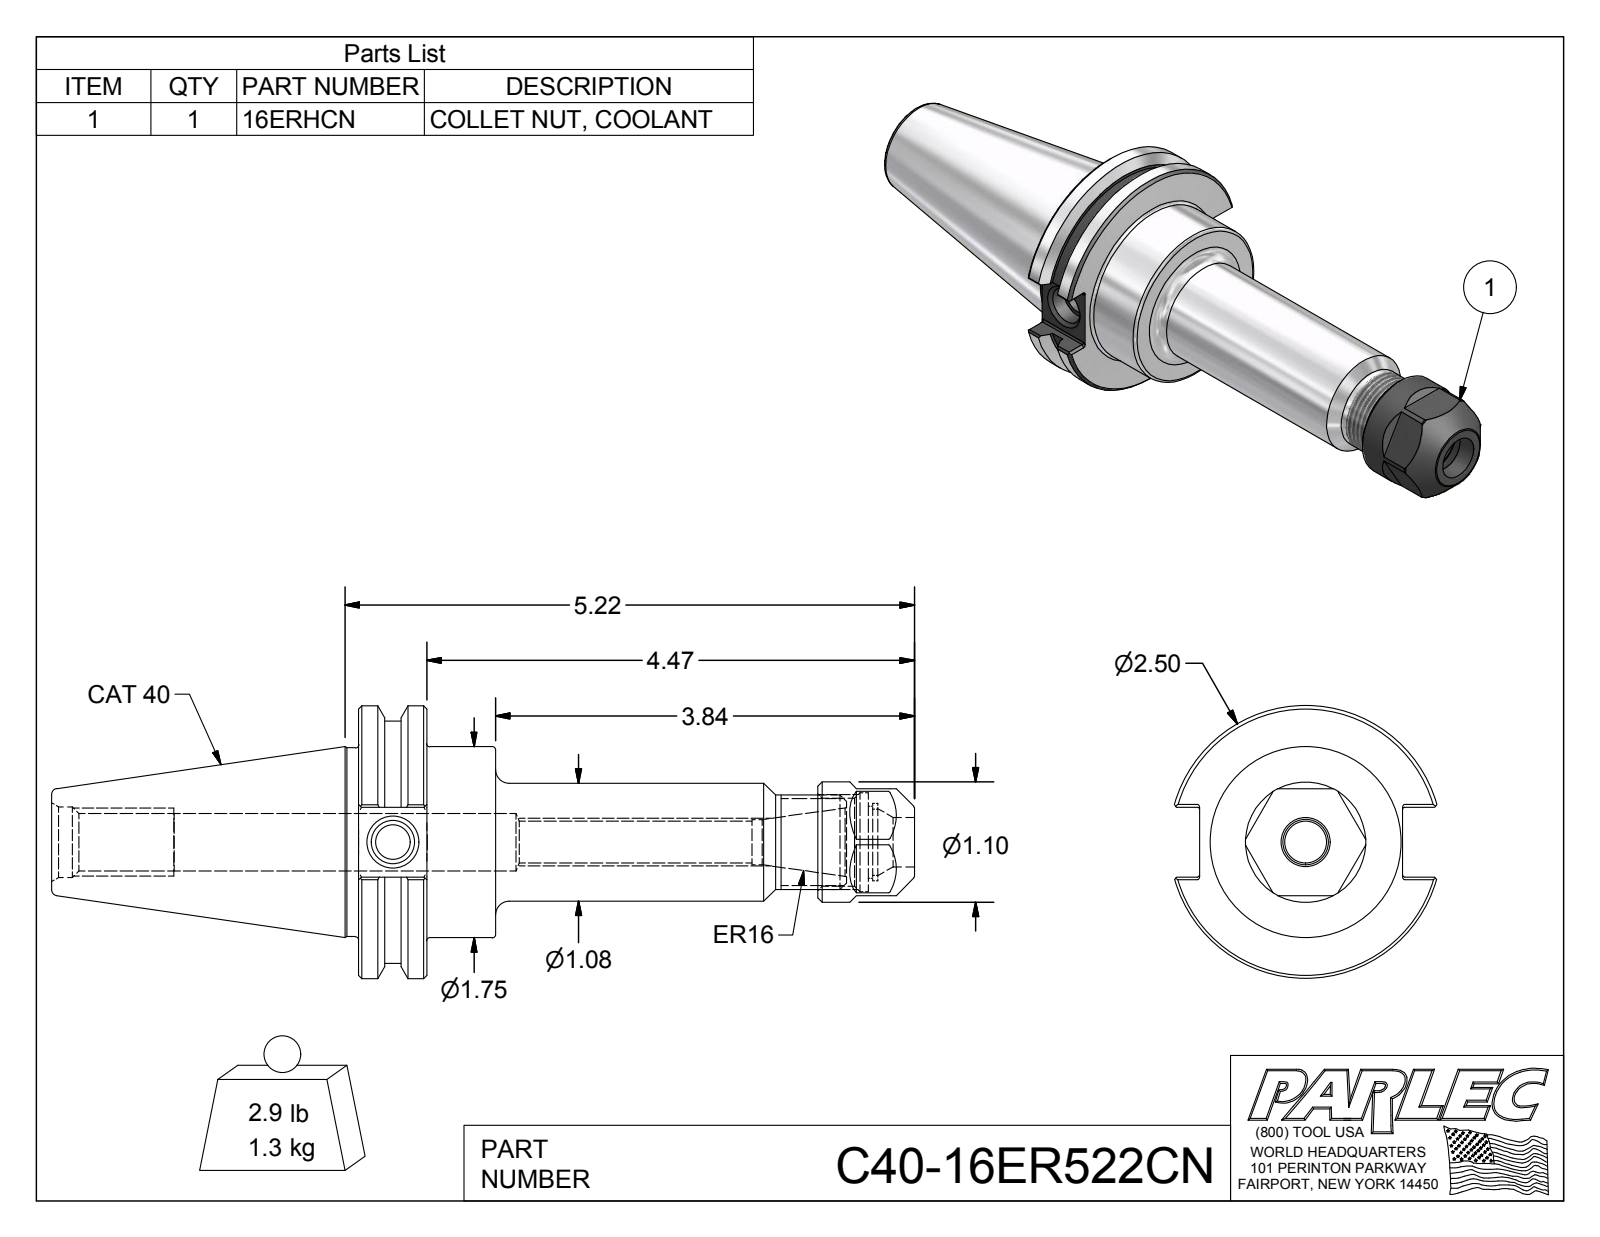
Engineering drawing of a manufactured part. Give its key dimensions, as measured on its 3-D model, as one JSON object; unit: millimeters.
{"part_name": "C40-16ER522CN; C40-16ER5-1; 16ERHCN", "step_written_by": "Autodesk Inventor 2012 (AUTOMOTIVE_DESIGN)", "units": "millimeters", "bodies": {"solids": 2, "faces": 122, "planar": 50, "cylindrical": 35, "other": 37}, "overall_size": [200.9, 63.5, 61], "volume_mm3": 166000, "surface_area_mm2": 36130, "round_holes": [[8, 1], [9.7, 1], [10.1, 1], [10.5, 1], [11.5, 1], [13.4, 1], [13.4, 1], [16.5, 1], [16.8, 1], [20.5, 1], [23, 1]], "round_bosses_or_shafts": [[63.5, 1], [56.4, 1], [44.5, 1], [43.9, 1], [28, 1], [27.4, 1], [22, 1]], "partial_cylinders_radius": [[0.5, 12], [9, 1]], "face_to_face_distances": [15.9, 31.9, 16, 24.9, 4.3, 20.5, 118.7, 102.8, 86.8, 16.3], "hole_center_spacings": [1.3]}
